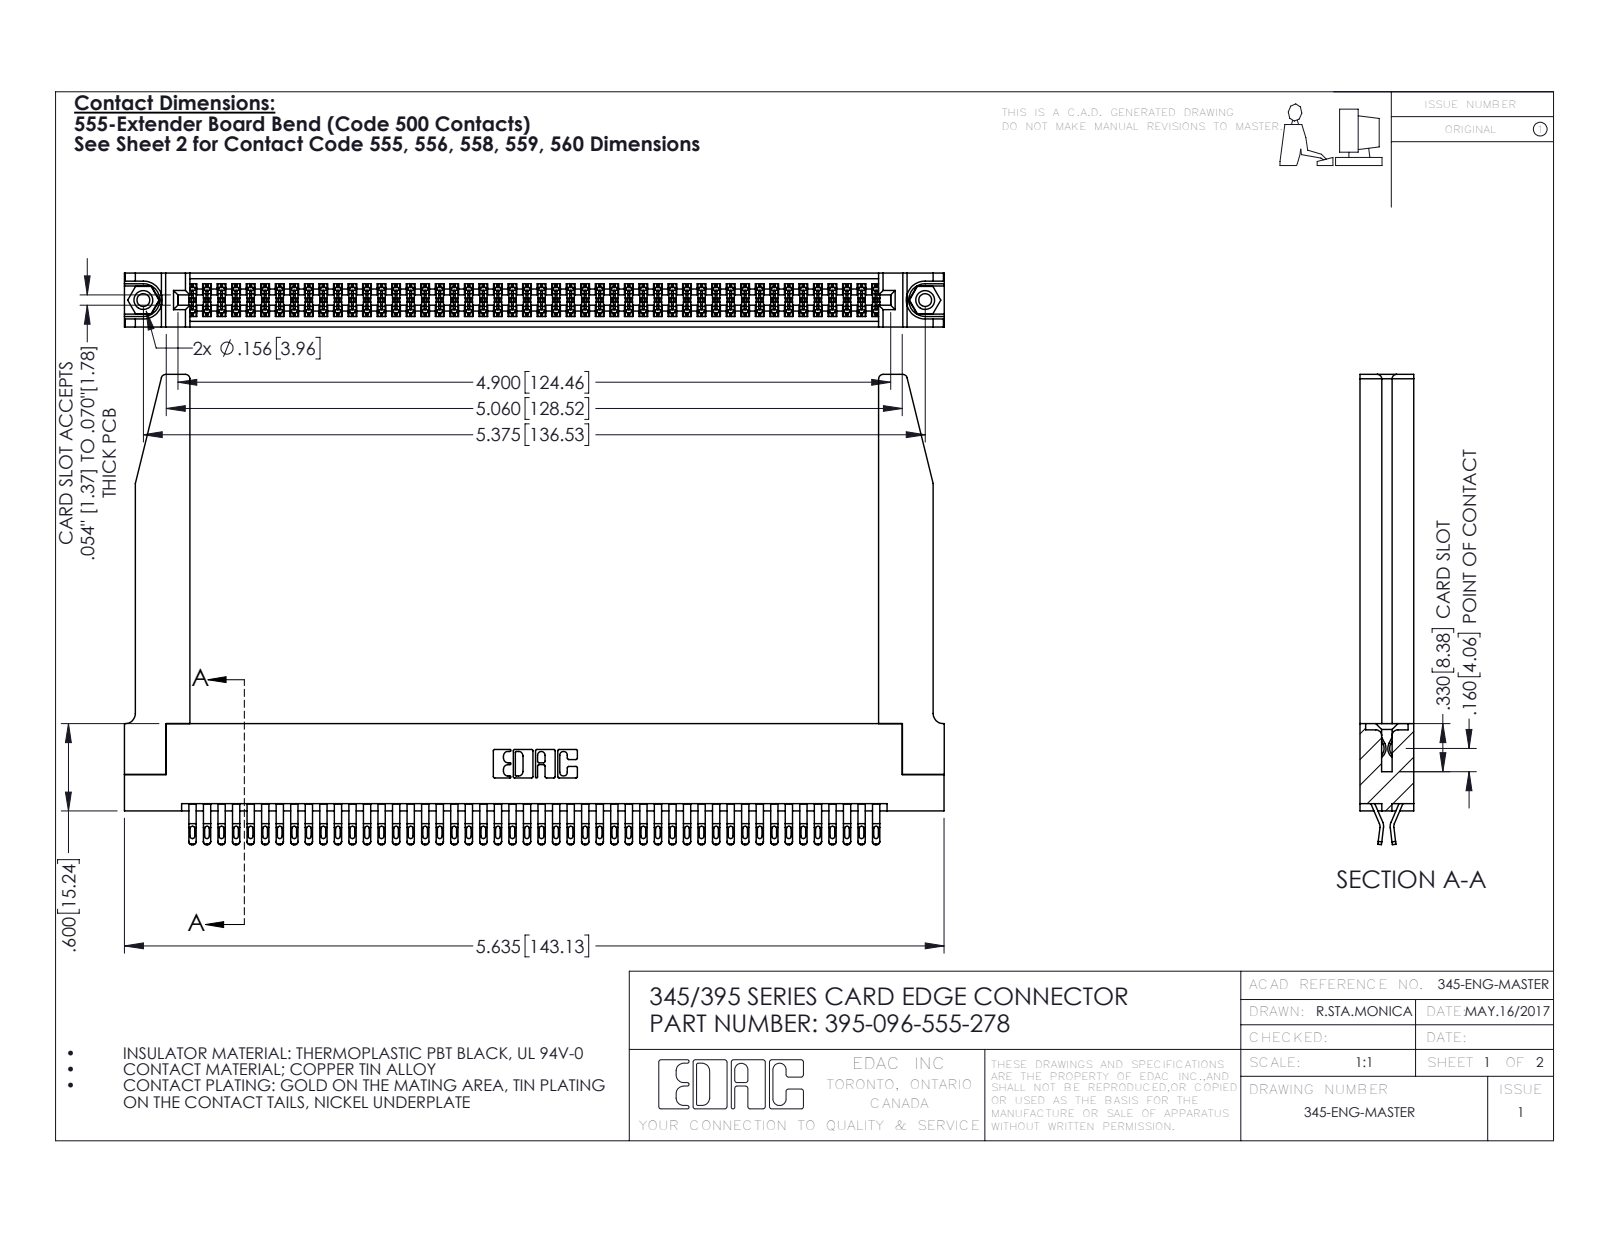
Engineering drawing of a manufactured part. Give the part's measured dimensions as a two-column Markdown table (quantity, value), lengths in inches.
| quantity | value |
| --- | --- |
| part name | 345-220-078_345-220-078; 345-250-001_345-250-001-102; 345-292-001_555 Tail; 395-096-555-278 (+1 more) |
| STEP written by | SolidWorks 2016 (CONFIG_CONTROL_DESIGN) |
| units | inches |
| bodies | 101 solids, 5736 faces (3198 planar, 2486 cylindrical, 52 other) |
| overall size | 5.636 × 3.232 × 0.37 |
| volume | 1.343 in³ |
| surface area | 44.91 in² |
| round holes (diameter × count) | 0.089 × 2, 0.125 × 2, 0.156 × 2, 0.064 × 1 |
| round bosses / shafts (diameter × count) | 0.155 × 2 |
| partial cylindrical surfaces (radius × count) | 0.016 × 240, 0.02 × 192, 0.006 × 144, 0.01 × 22, 0.03 × 8, 0.007 × 6, 0.031 × 6, 0.026 × 3 |
| main face-to-face distances | 0.072, 0.37, 0.298, 0.025, 0.2, 0.098, 0.272, 0.225, 0.15, 0.148 |
| hole center spacings | 0.27, 5.139, 5.375 |
